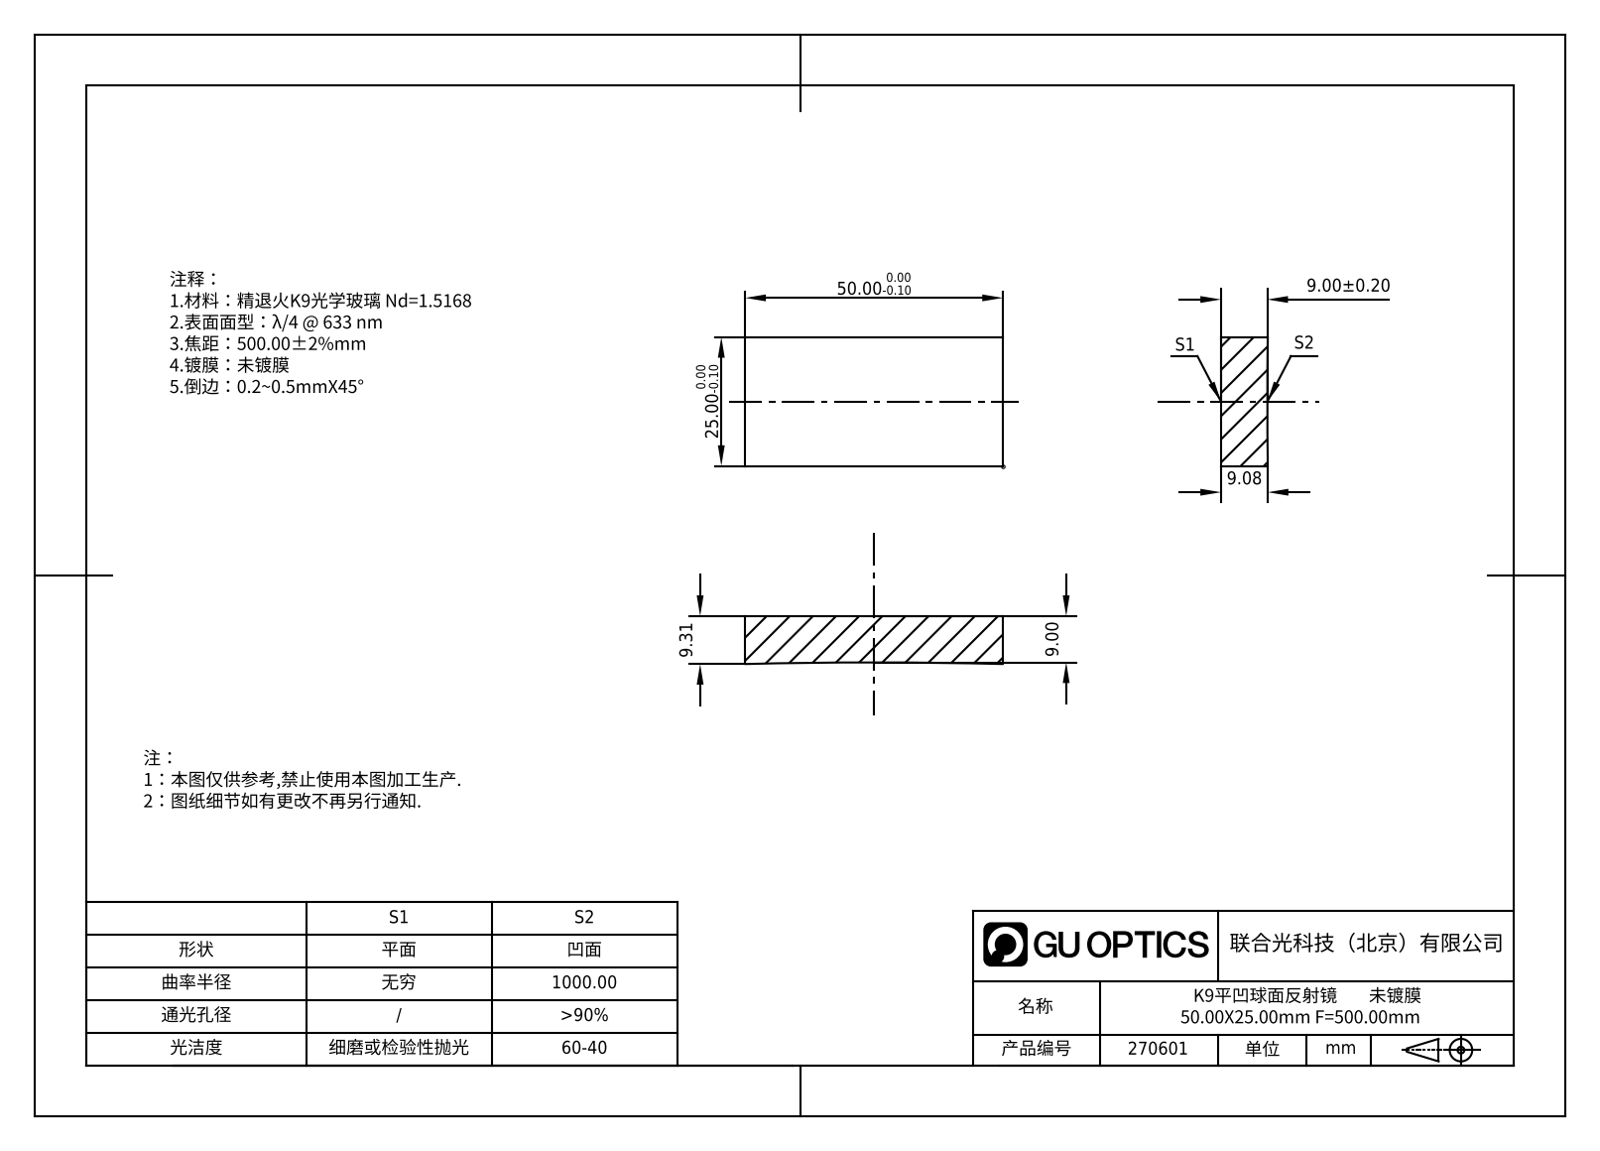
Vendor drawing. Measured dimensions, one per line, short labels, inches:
name: GM13-50x25-500
written by: SolidWorks 2022 (AUTOMOTIVE_DESIGN)
unit: in
bodies: 1 solid, 7 faces (5 planar, 0 cylindrical, 2 other)
size: 1.969 × 0.984 × 0.37
volume: 0.696 in³; area: 6.022 in²
face distances: 0.984, 1.969
